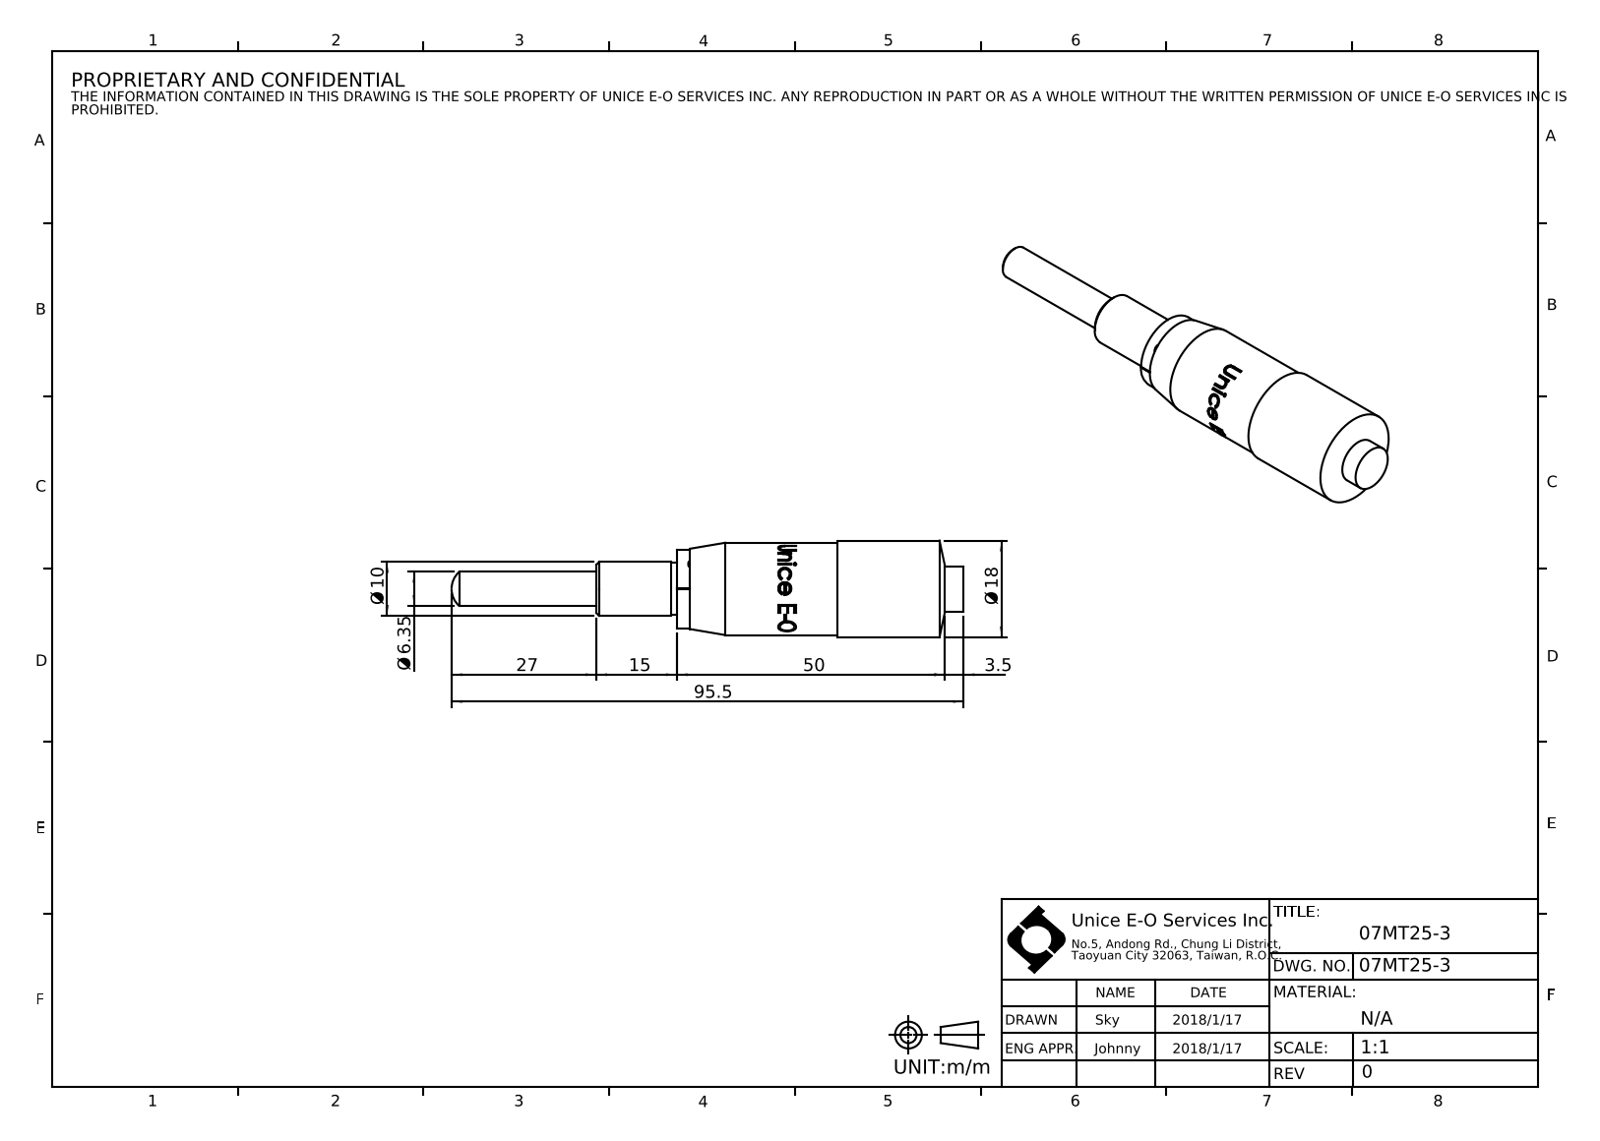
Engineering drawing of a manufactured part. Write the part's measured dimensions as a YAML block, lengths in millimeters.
part_name: "07MT25-3"
step_written_by: "SolidWorks 2016 (AUTOMOTIVE_DESIGN)"
units: millimeters
bodies: {solids: 0, faces: 80, planar: 20, cylindrical: 27, other: 33}
overall_size: [95.5, 18, 18]
round_bosses_or_shafts:
  - {diameter: 18, count: 1}
  - {diameter: 17.2, count: 1}
  - {diameter: 14.6, count: 1}
  - {diameter: 10, count: 1}
  - {diameter: 9.75, count: 1}
  - {diameter: 8.5, count: 1}
  - {diameter: 6.35, count: 1}
partial_cylinders:
  - {radius: 8.55, count: 1}
face_to_face_distances: [53.5, 15, 68.5, 45, 30, 23.5, 17.5, 2.5, 27.5, 51]
